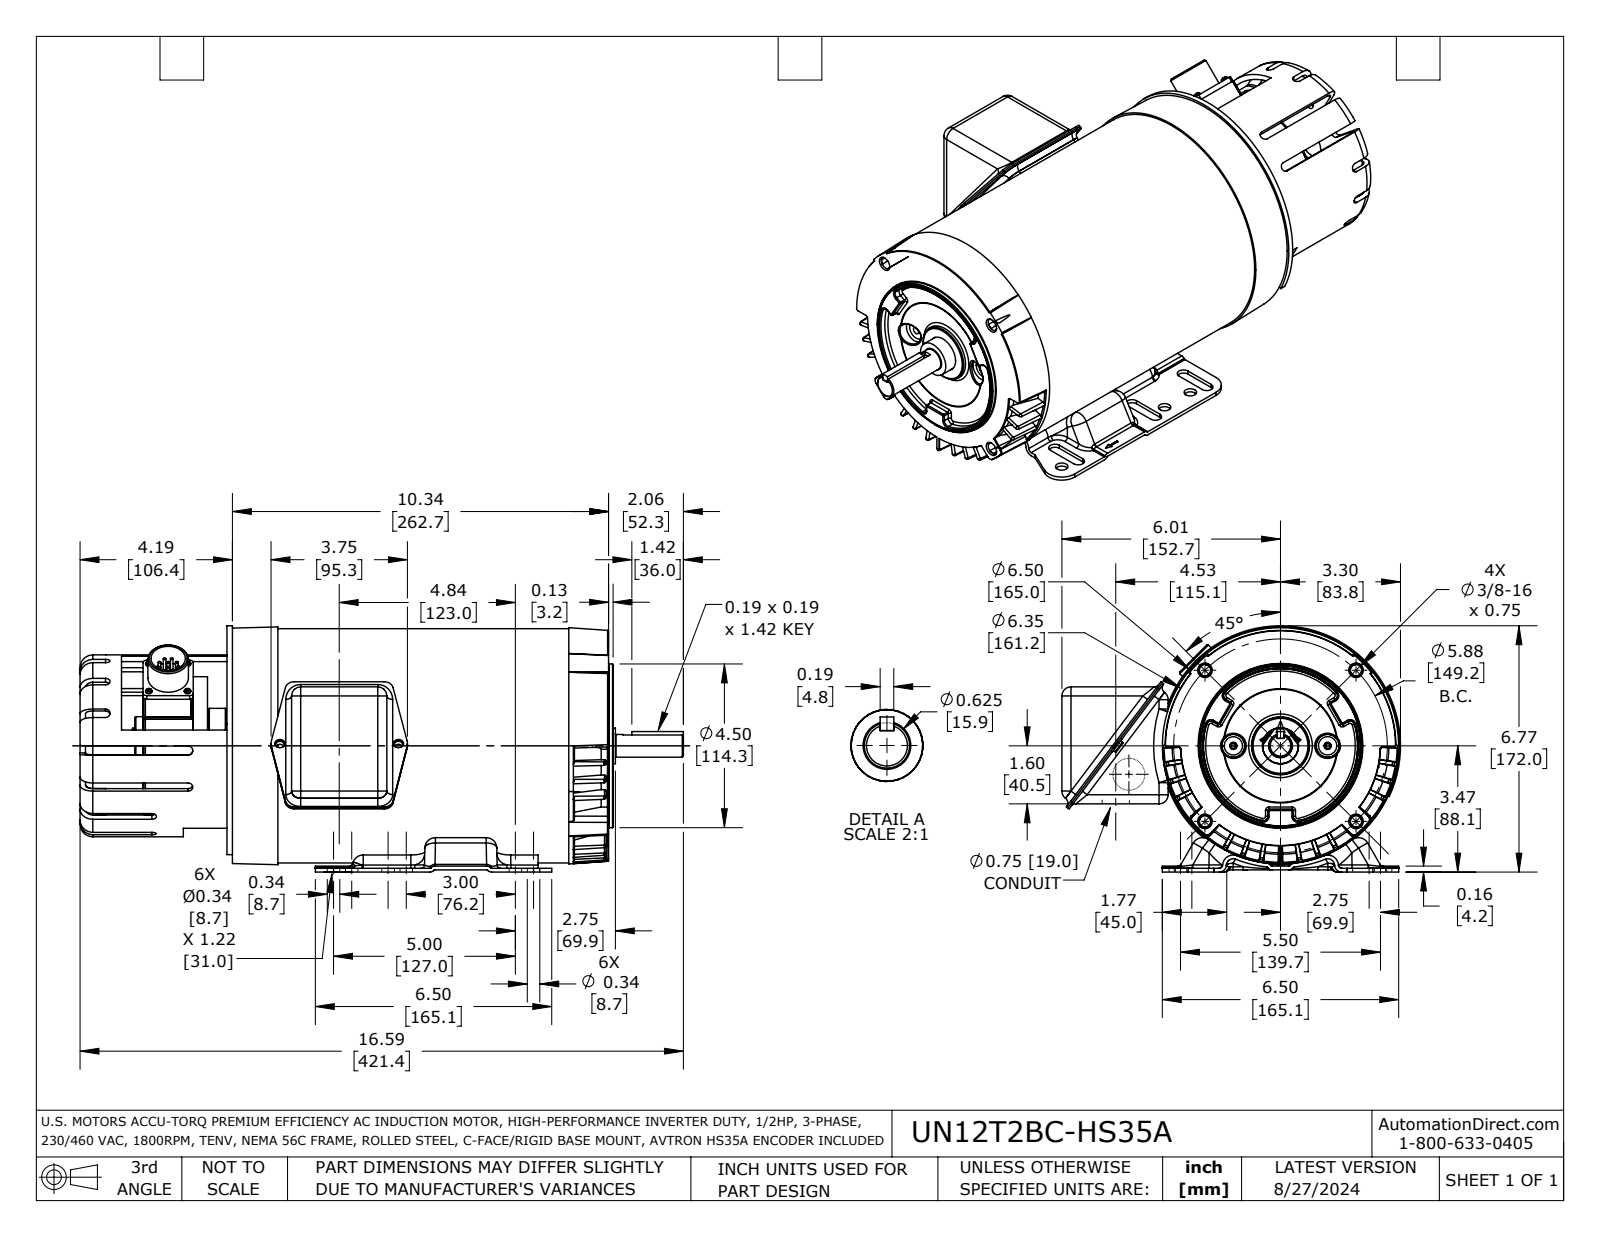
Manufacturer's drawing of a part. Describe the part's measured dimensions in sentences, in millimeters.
The part is named "UN12T2BC-HS35A". Its 3-D file was written by "SolidWorks 2021 (AUTOMOTIVE_DESIGN)". It is 26 solids with 3051 faces: 756 planar, 717 cylindrical and 1578 other. Overall it measures 421.4 by 236.5 by 172 millimeters. Its volume is 1 680 000 cubic millimeters and its surface area 752 300 square millimeters. Round holes: 8 of diameter 6.4, 6 of diameter 8.7, 6 of diameter 10.2, 4 of diameter 3, 4 of diameter 5.1, 4 of diameter 7.7, 4 of diameter 10.7, 4 of diameter 14, 3 of diameter 3.5, 2 of diameter 2.5, 2 of diameter 4.4, 2 of diameter 5.8. Round bosses or shafts: 8 of diameter 1.8, 4 of diameter 4.4, 4 of diameter 3, 3 of diameter 3.8, 2 of diameter 8.3, 2 of diameter 1.8, 1 of diameter 163.6, 1 of diameter 160.4. Partial cylindrical surfaces (rounded edges, fillets, slot ends): 91 of radius 1.6, 71 of radius 0.8, 42 of radius 3.2, 26 of radius 6.4, 18 of radius 5.1, 13 of radius 2.4, 12 of radius 1.2, 12 of radius 4.4. The main face-to-face distances are 1.2, 27.4, 34.9, 62.4, 3.8, 102.6, 2.6, 3, 13.5, 1.5. The hole center spacings are 53.3, 57, 86.8, 110.5, 137.7, 52.7, 56.7, 56.7.
